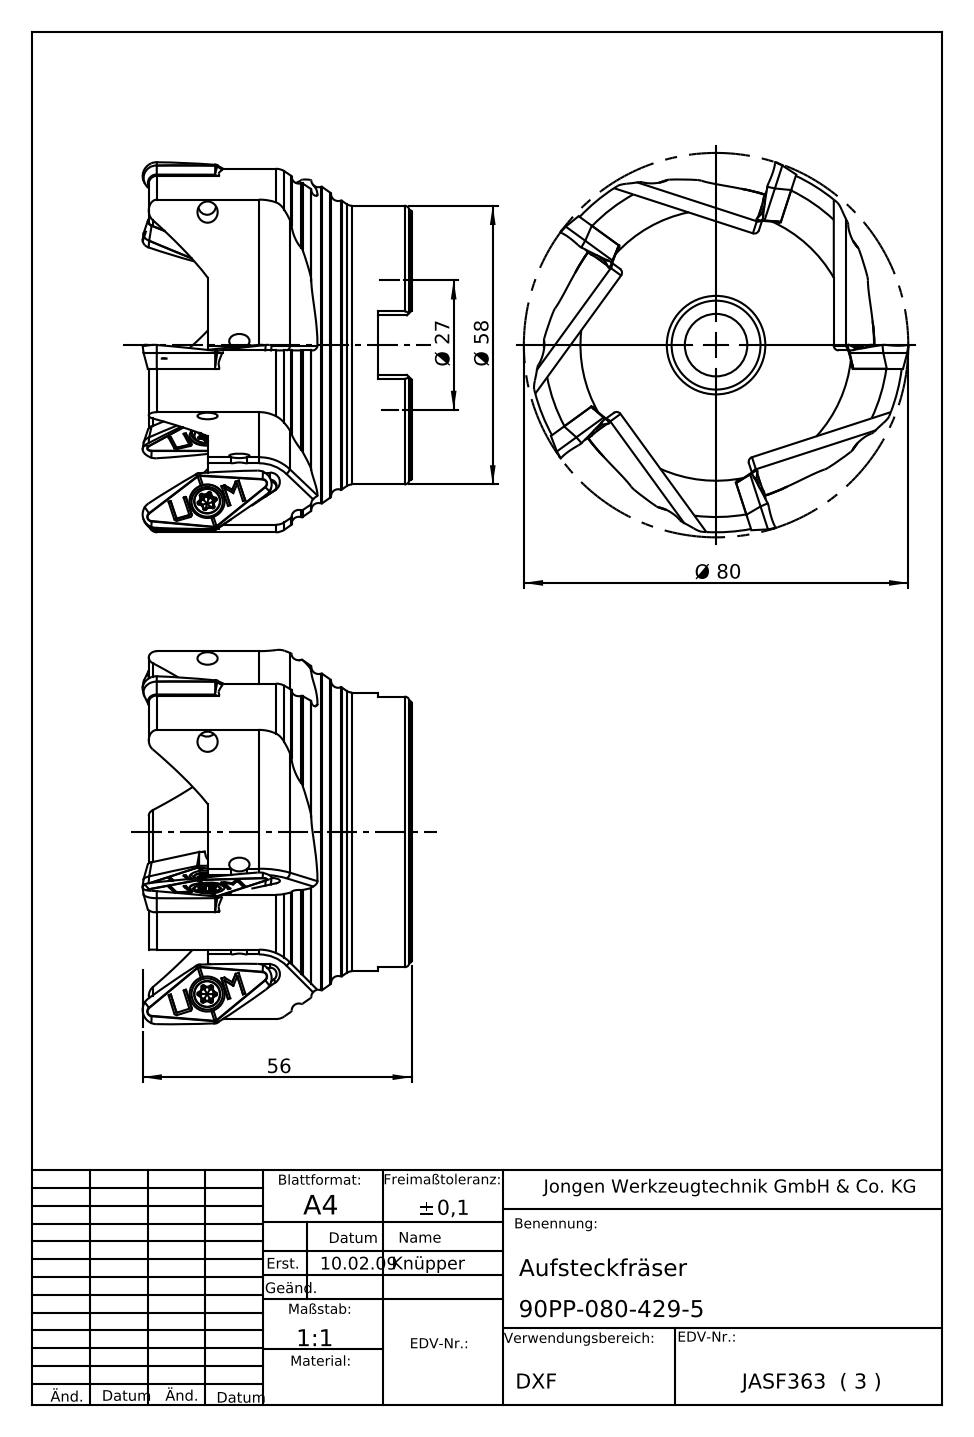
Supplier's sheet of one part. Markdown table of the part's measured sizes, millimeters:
| quantity | value |
| --- | --- |
| part name | 90PP-080-429-5 |
| STEP written by | SolidWorks 2010 (AUTOMOTIVE_DESIGN) |
| units | millimeters |
| bodies | 1 solid, 198 faces (39 planar, 50 cylindrical, 109 other) |
| overall size | 80.14 × 80.14 × 56 |
| volume | 143 140 mm³ |
| surface area | 31 704 mm² |
| round holes (diameter × count) | 3 × 5, 13 × 1, 18.5 × 1, 26.85 × 1, 27.15 × 1, 27.3 × 1 |
| round bosses / shafts (diameter × count) | 77.9 × 1, 58 × 1 |
| partial cylindrical surfaces (radius × count) | 1 × 10, 9 × 5 |
| main face-to-face distances | 12.3, 54.72, 42.42, 47.72, 35.42, 7, 29.72, 17.42, 18, 25 |
